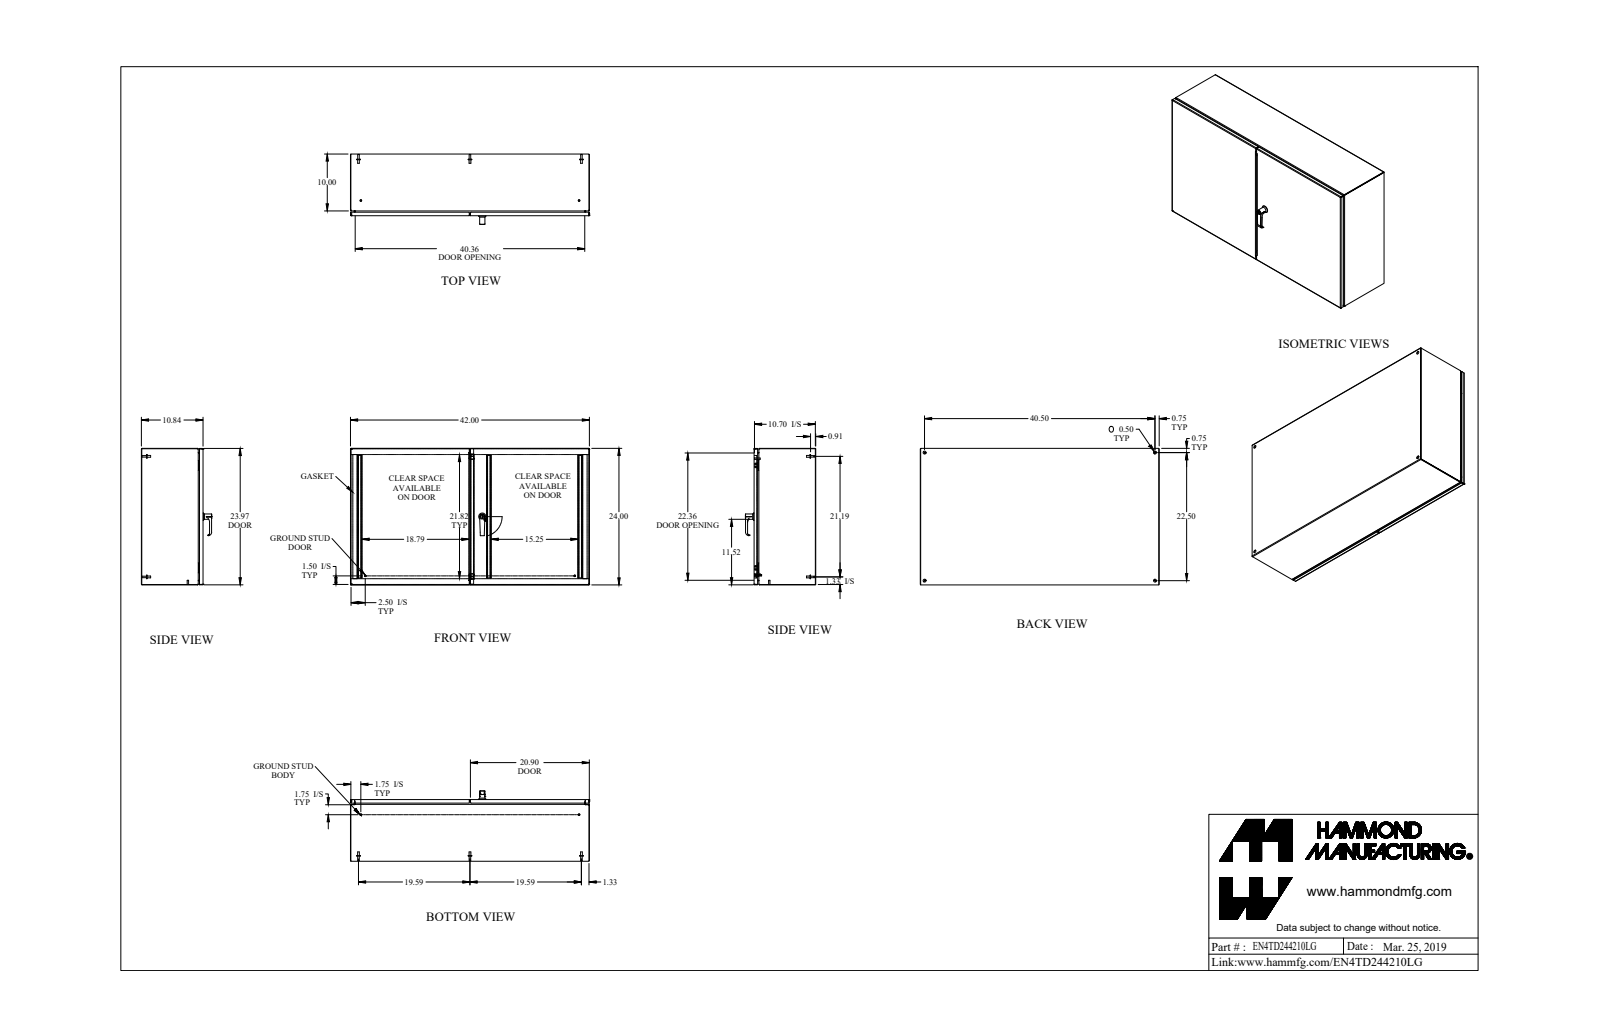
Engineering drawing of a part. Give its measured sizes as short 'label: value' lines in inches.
name: EN4TD244210LG
written by: SolidWorks 2018 (AUTOMOTIVE_DESIGN)
unit: in
bodies: 77 solids, 1935 faces (883 planar, 714 cylindrical, 338 other)
size: 42 × 24 × 12.372
volume: 306.7 in³; area: 7 984 in²
holes: 5× ⌀0.196, 4× ⌀0.176, 4× ⌀0.5, 3× ⌀0.24, 3× ⌀0.242, 3× ⌀0.265, 2× ⌀0.172, 2× ⌀0.25, 2× ⌀0.256, 2× ⌀0.26, 2× ⌀0.265, 2× ⌀0.313
bosses: 12× ⌀0.25, 8× ⌀0.313, 6× ⌀0.625, 6× ⌀0.27, 4× ⌀0.51, 4× ⌀0.281, 4× ⌀0.156, 3× ⌀0.75
rounds: 26× R0.036, 26× R0.108, 20× R0.094, 19× R0.063, 18× R0.043, 18× R0.081, 16× R0.02, 15× R0.016
face distances: 0.072, 10.77, 10.698, 10.842, 23.928, 41.928, 23.856, 24, 41.856, 42
hole spacings: 0.787, 10.188, 21.296, 22.5, 22.756, 25.082, 40.5, 46.33
